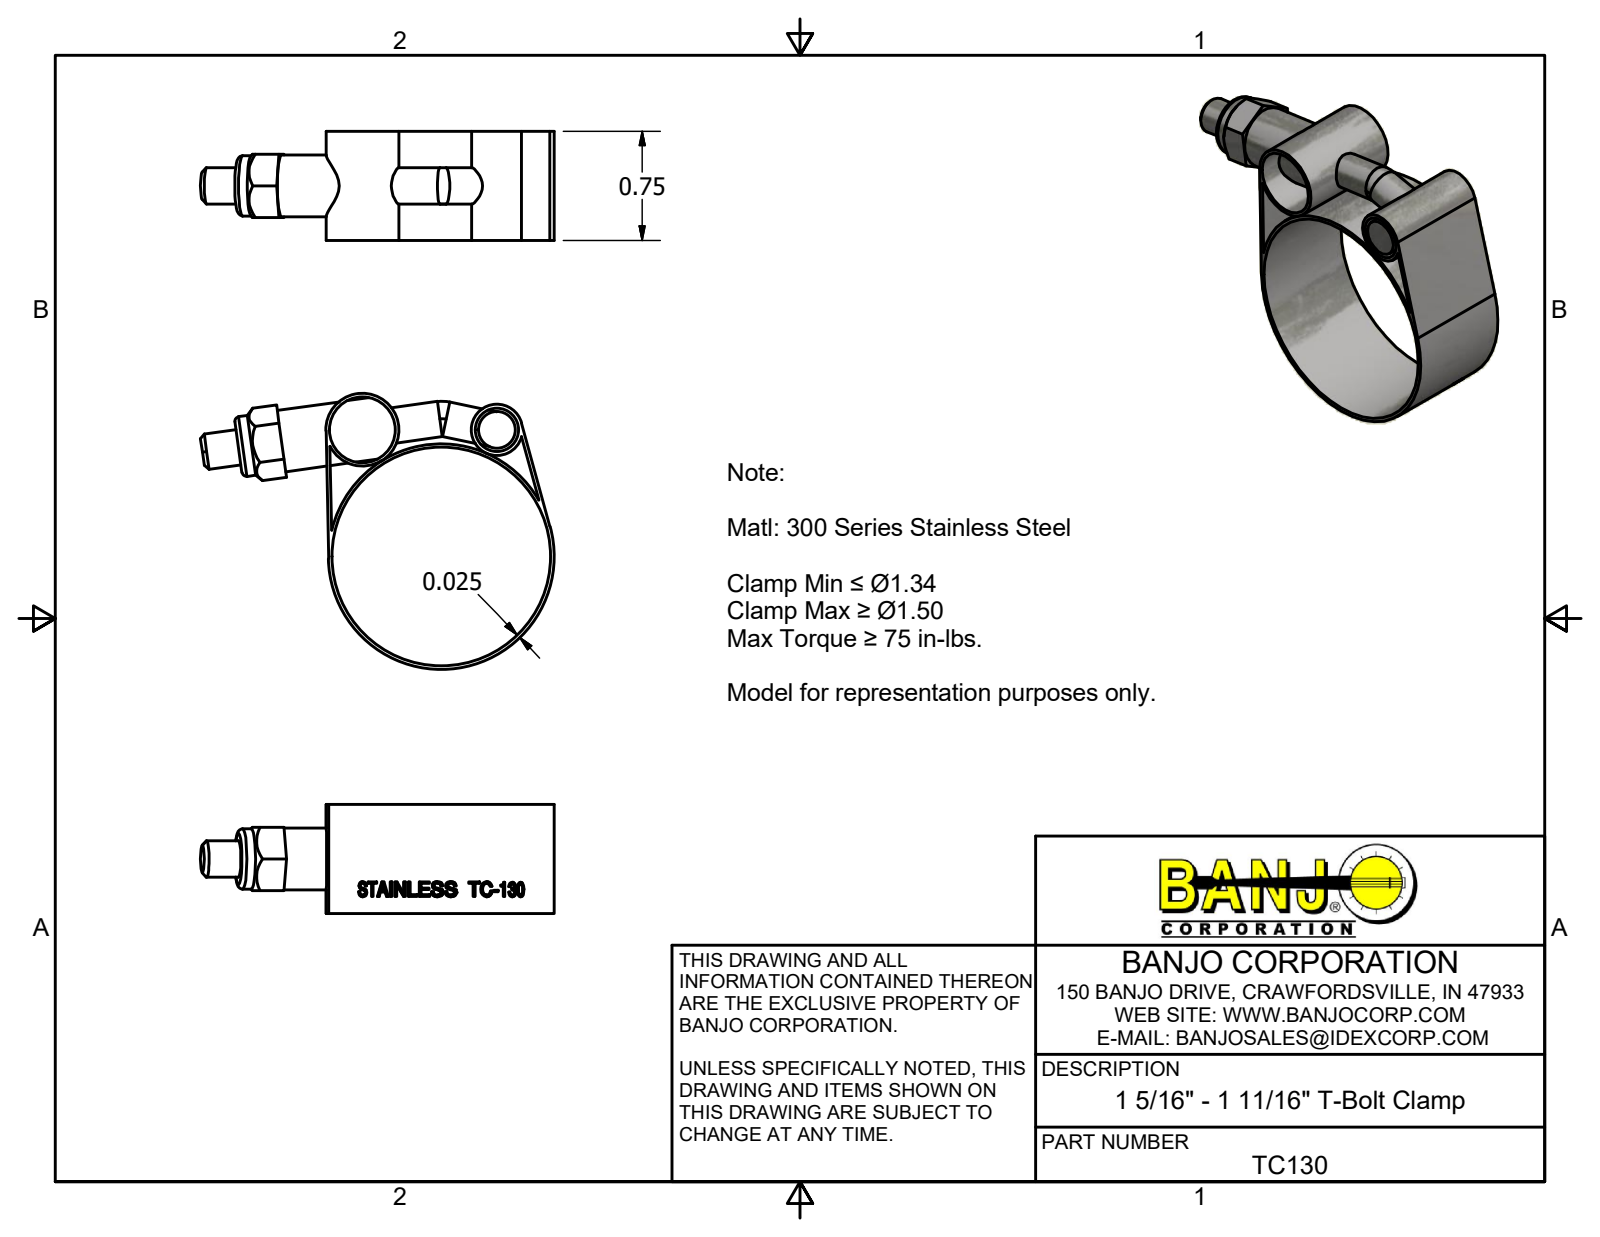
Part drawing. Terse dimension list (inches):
name: TC130
written by: Autodesk Inventor 2018 (AUTOMOTIVE_DESIGN)
unit: in
bodies: 1 solid, 239 faces (94 planar, 39 cylindrical, 106 other)
size: 2.43 × 1.895 × 0.75
volume: 0.382 in³; area: 16.57 in²
holes: 1× ⌀0.3, 1× ⌀0.45, 1× ⌀1.5
bosses: 1× ⌀1.55, 1× ⌀0.5, 1× ⌀0.425, 1× ⌀0.415, 1× ⌀0.35, 1× ⌀0.25
rounds: 1× R0.77
face distances: 0.025, 0.75, 0.435, 0.157, 0.592, 0.435, 0.25, 0.55, 0.3, 0.039
hole spacings: 0.925, 0.95, 1.025
